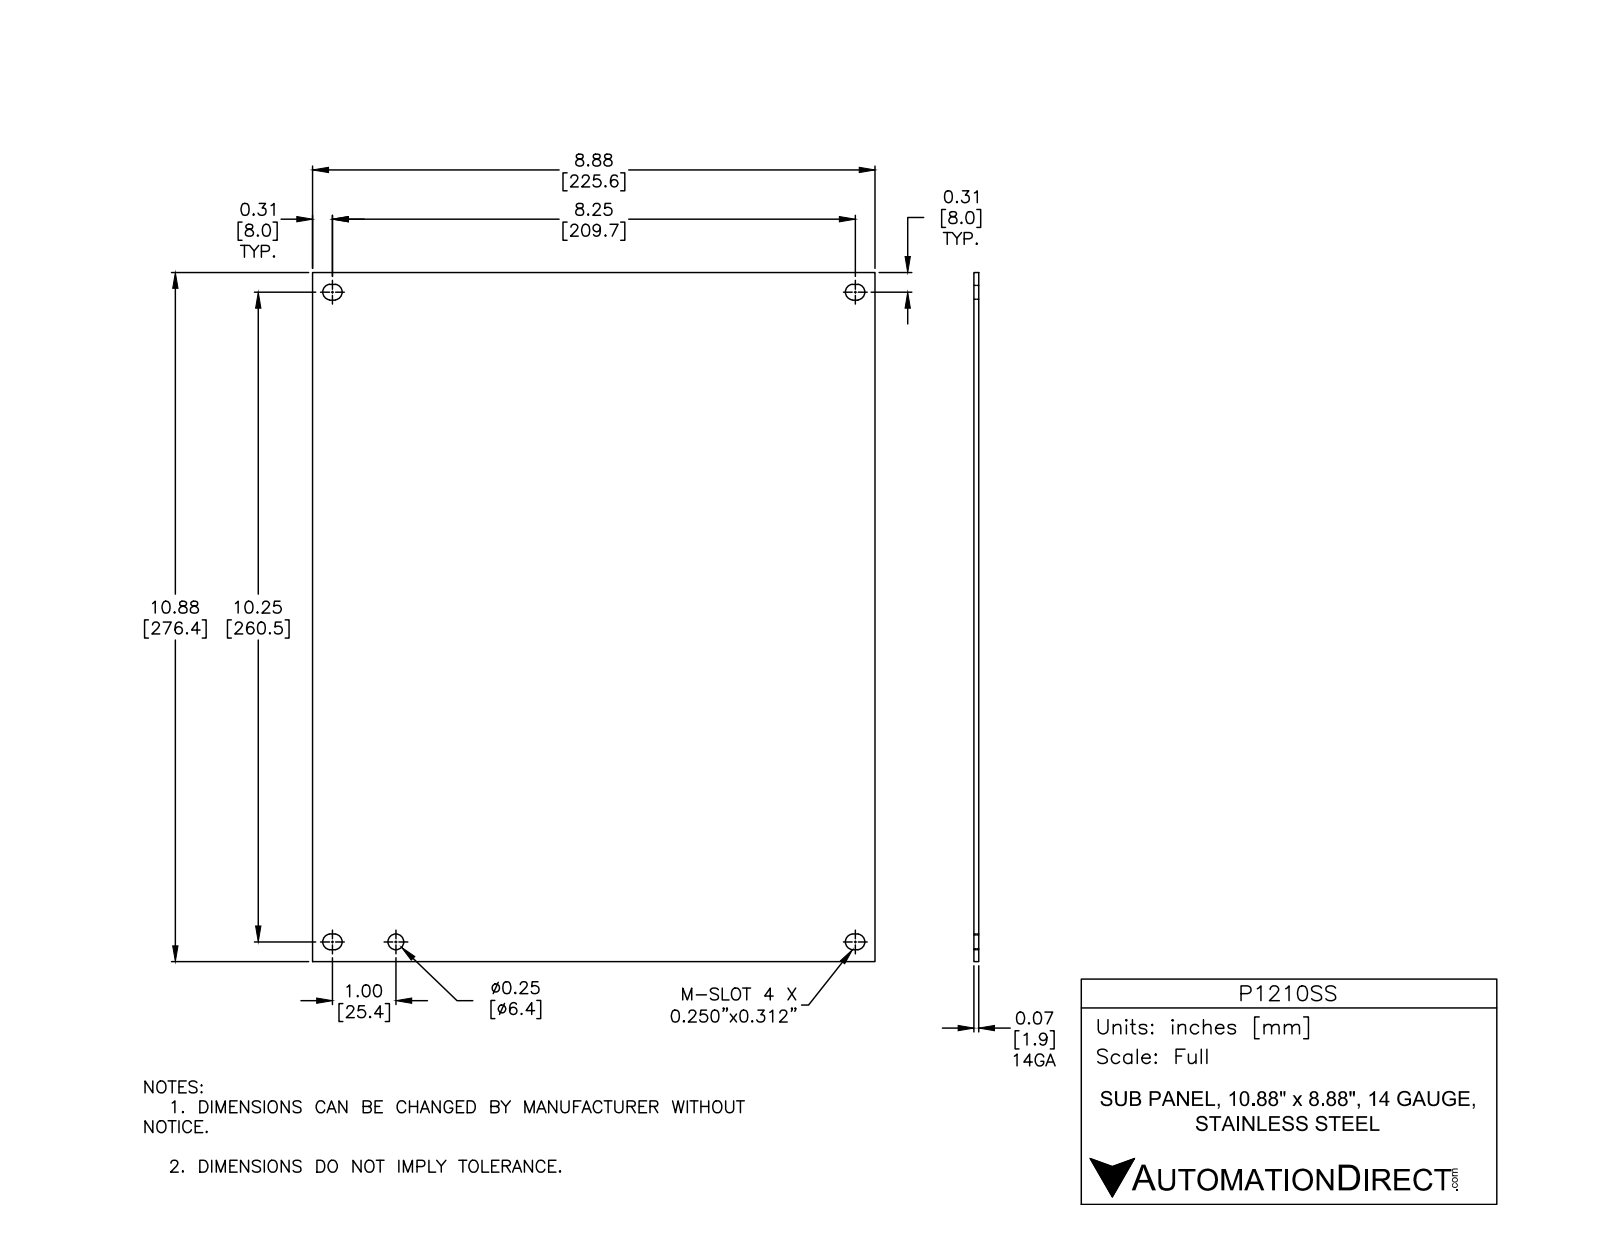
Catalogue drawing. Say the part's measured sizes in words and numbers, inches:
The part is named "P1210SS". Its 3-D file was written by "Autodesk Inventor 2012 (AUTOMOTIVE_DESIGN)". It is 1 solid with 23 faces: 14 planar, 9 cylindrical and 0 other. Overall it measures 10.88 by 8.88 by 0.074 inches. Its volume is 7.127 cubic inches and its surface area 195.9 square inches. Round holes: 1 of diameter 0.25. Partial cylindrical surfaces (rounded edges, fillets, slot ends): 8 of radius 0.125. The main face-to-face distances are 0.074, 8.88, 10.88, 0.25, 10.254, 0.188, 0.438, 10.692, 10.442, 10.442.
